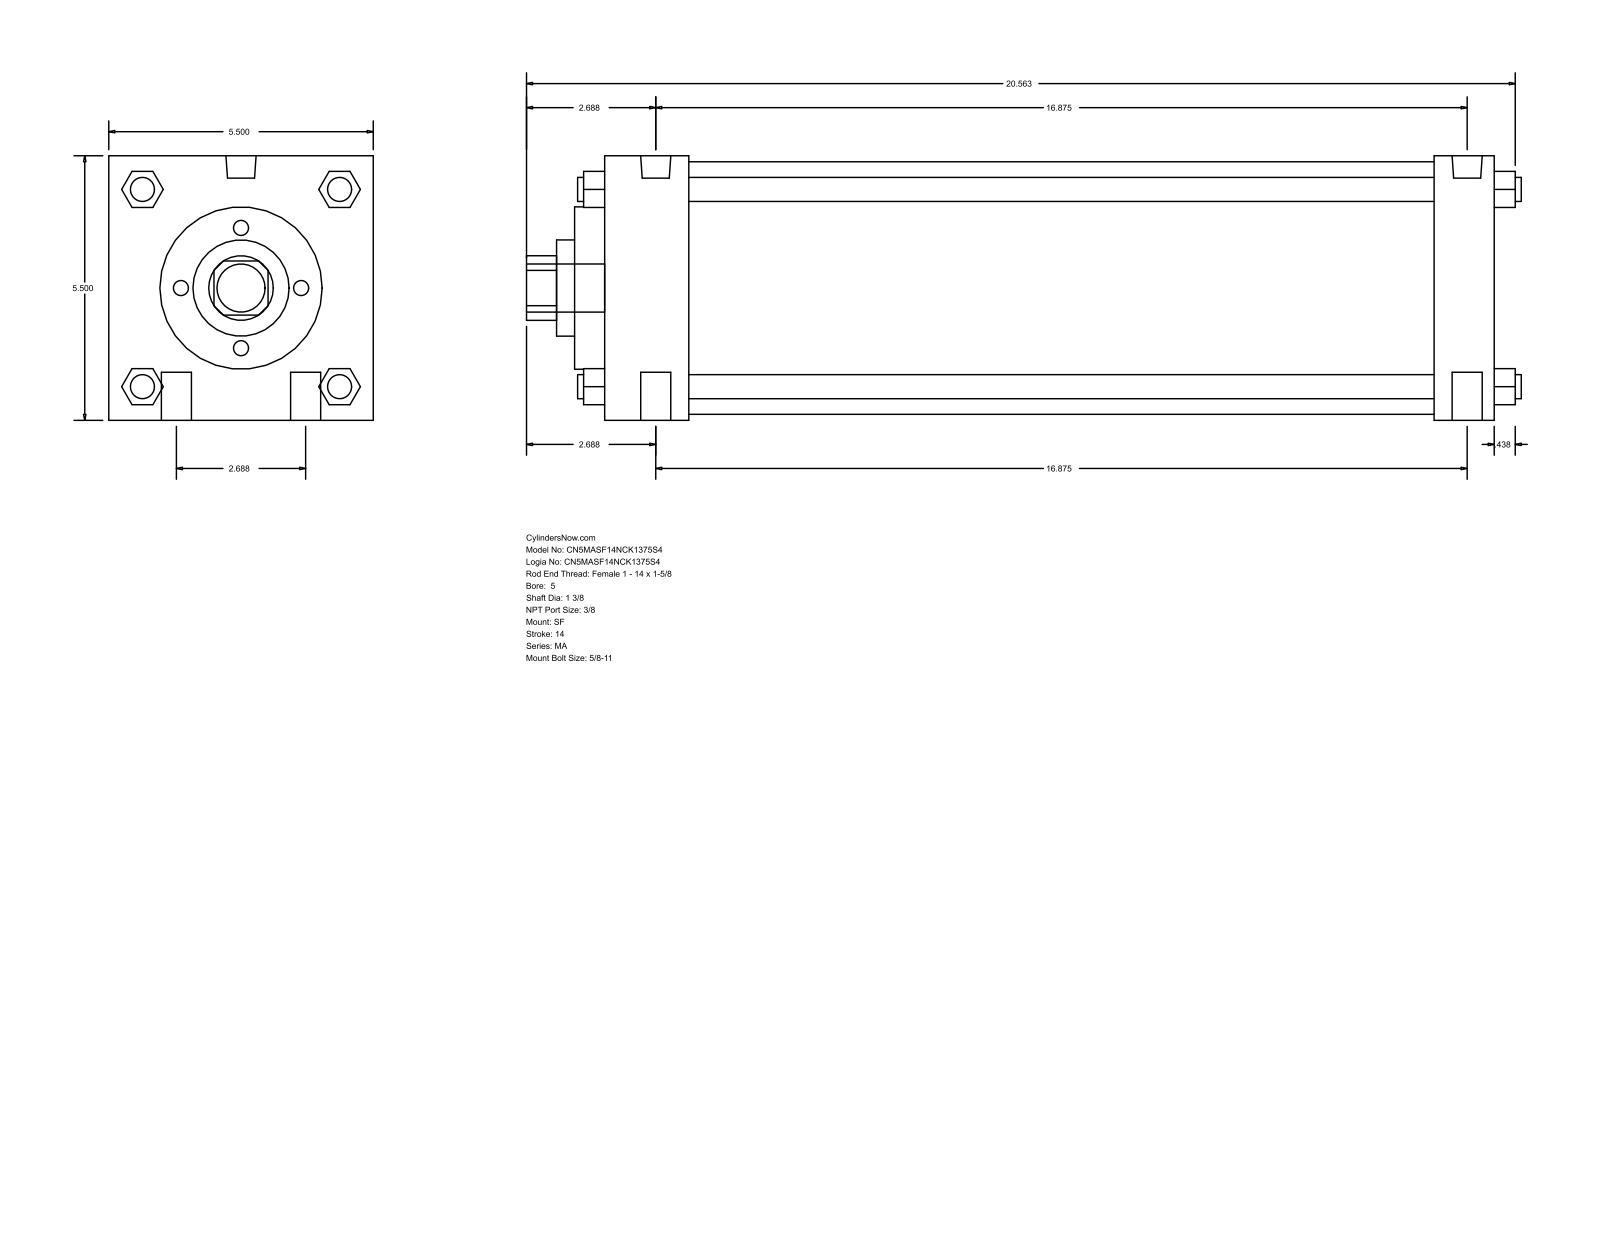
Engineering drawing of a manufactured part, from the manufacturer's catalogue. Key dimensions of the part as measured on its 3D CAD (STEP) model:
Part name (STEP PRODUCT): MA_SF__0500_1.375
STEP written by: GSSL Pune (CONFIG_CONTROL_DESIGN)
Units: millimetres
Bodies: 0 solids, 126 faces (95 planar, 31 cylindrical, 0 other)
Overall size (bounding box): 525.46 × 139.7 × 139.7
Round holes (diameter × count): ⌀34.92 ×1, ⌀50.8 ×1, ⌀85.72 ×1, ⌀133.35 ×1
Round bosses / shafts (diameter × count): ⌀15.88 ×4, ⌀12.7 ×4, ⌀15.93 ×2, ⌀11.11 ×2, ⌀25.4 ×1
Partial cylindrical surfaces — rounded edges, fillets, slot ends (radius × count): R17.06 ×1
Main face-to-face distances: 139.7, 469.91, 44.45, 438.16, 393.71, 425.46, 31.75, 15.87, 60.32, 454.03
